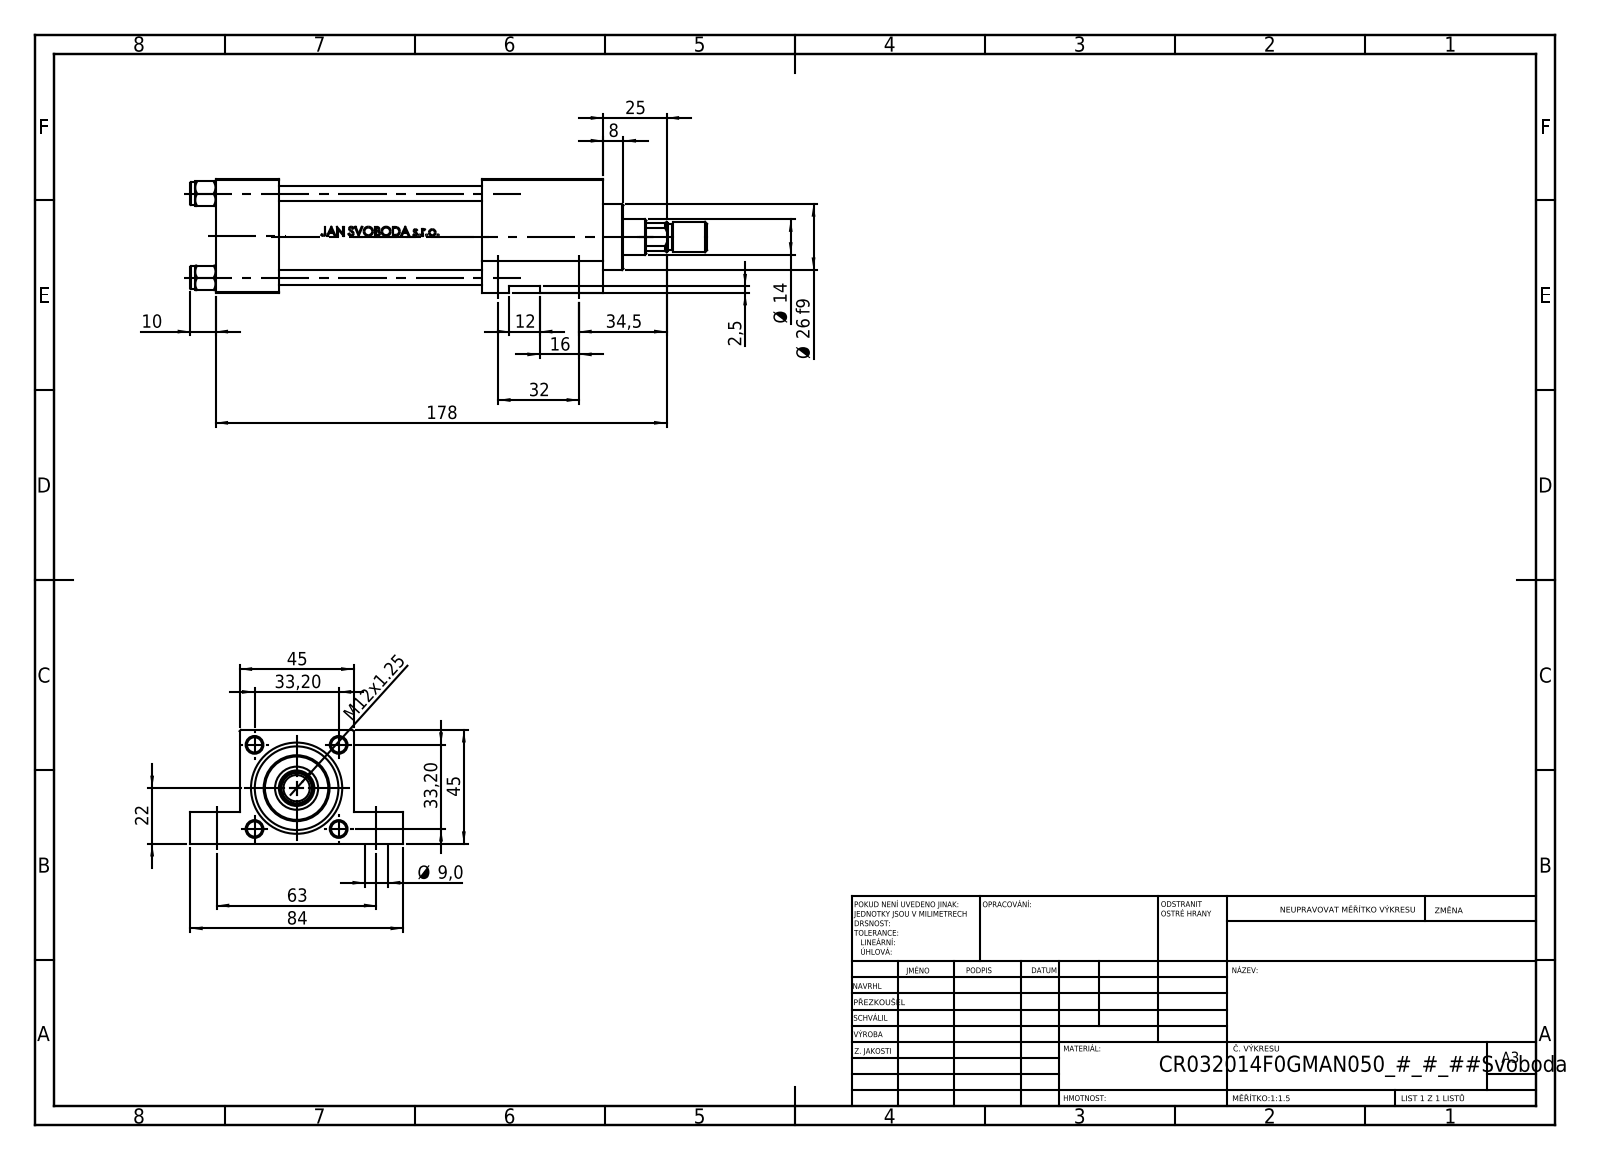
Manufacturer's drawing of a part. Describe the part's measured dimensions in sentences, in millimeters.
The part is named "V215CR_VCP_F; V215CR_F_Body; V215CR_F_TYCINKA; ROD_END_AH (+2 more)". Its 3-D file was written by "SolidWorks 2019 (CONFIG_CONTROL_DESIGN)". It is 12 solids with 1116 faces: 440 planar, 130 cylindrical and 546 other. Overall it measures 204 by 84 by 45 millimeters. Its volume is 231 550 cubic millimeters and its surface area 83 742 square millimeters. Round holes: 4 of diameter 6, 2 of diameter 7, 2 of diameter 9, 2 of diameter 9, 2 of diameter 20, 1 of diameter 6.5, 1 of diameter 13, 1 of diameter 13.16, 1 of diameter 14, 1 of diameter 17, 1 of diameter 24, 1 of diameter 32. Round bosses or shafts: 4 of diameter 9, 1 of diameter 38, 1 of diameter 26, 1 of diameter 12, 1 of diameter 10. Partial cylindrical surfaces (rounded edges, fillets, slot ends): 1 of radius 6.5. The main face-to-face distances are 45, 25, 128, 153, 32.5, 105, 80, 48, 12.5, 10. The hole center spacings are 33.2, 23.13, 23.83, 32, 46.95, 63, 70.66, 105.5.
